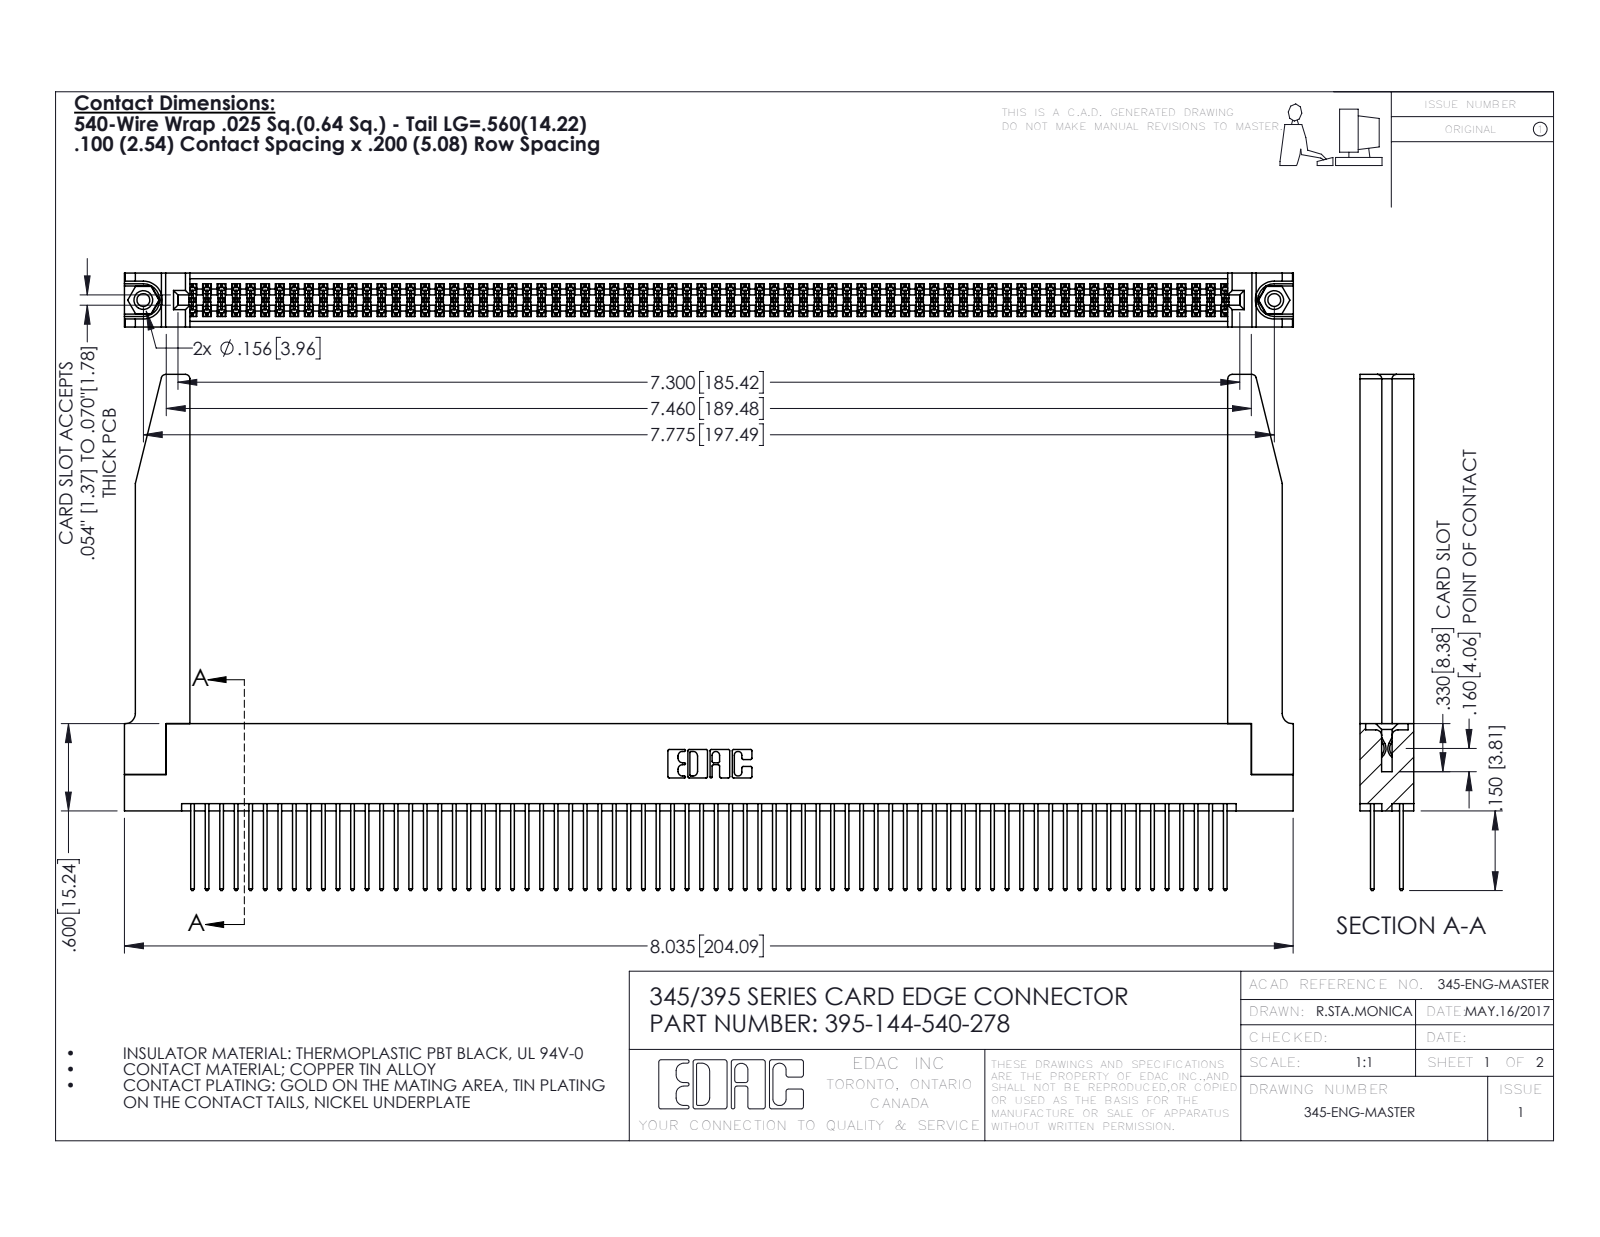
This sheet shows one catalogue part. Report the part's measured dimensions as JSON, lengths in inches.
{"part_name": "345-292-001_345-293-140; 395-144-540-278; 345 Part_Flush Mounting Lugs - 0.156 Dia-TH; 345-250-001_345-250-001-102 (+1 more)", "step_written_by": "SolidWorks 2016 (CONFIG_CONTROL_DESIGN)", "units": "inches", "bodies": {"solids": 149, "faces": 7560, "planar": 4974, "cylindrical": 2534, "other": 52}, "overall_size": [8.036, 3.547, 0.37], "volume_in3": 1.734, "surface_area_in2": 62.74, "round_holes": [[0.089, 2], [0.125, 2], [0.156, 2], [0.064, 1]], "round_bosses_or_shafts": [[0.155, 2]], "partial_cylinders_radius": [[0.006, 216], [0.01, 144], [0.01, 22], [0.03, 8], [0.007, 6], [0.031, 6], [0.026, 3], [0.014, 2]], "face_to_face_distances": [0.072, 0.298, 0.2, 0.37, 0.098, 0.272, 0.025, 0.225, 0.175, 0.149], "hole_center_spacings": [0.27, 7.539, 7.775]}
